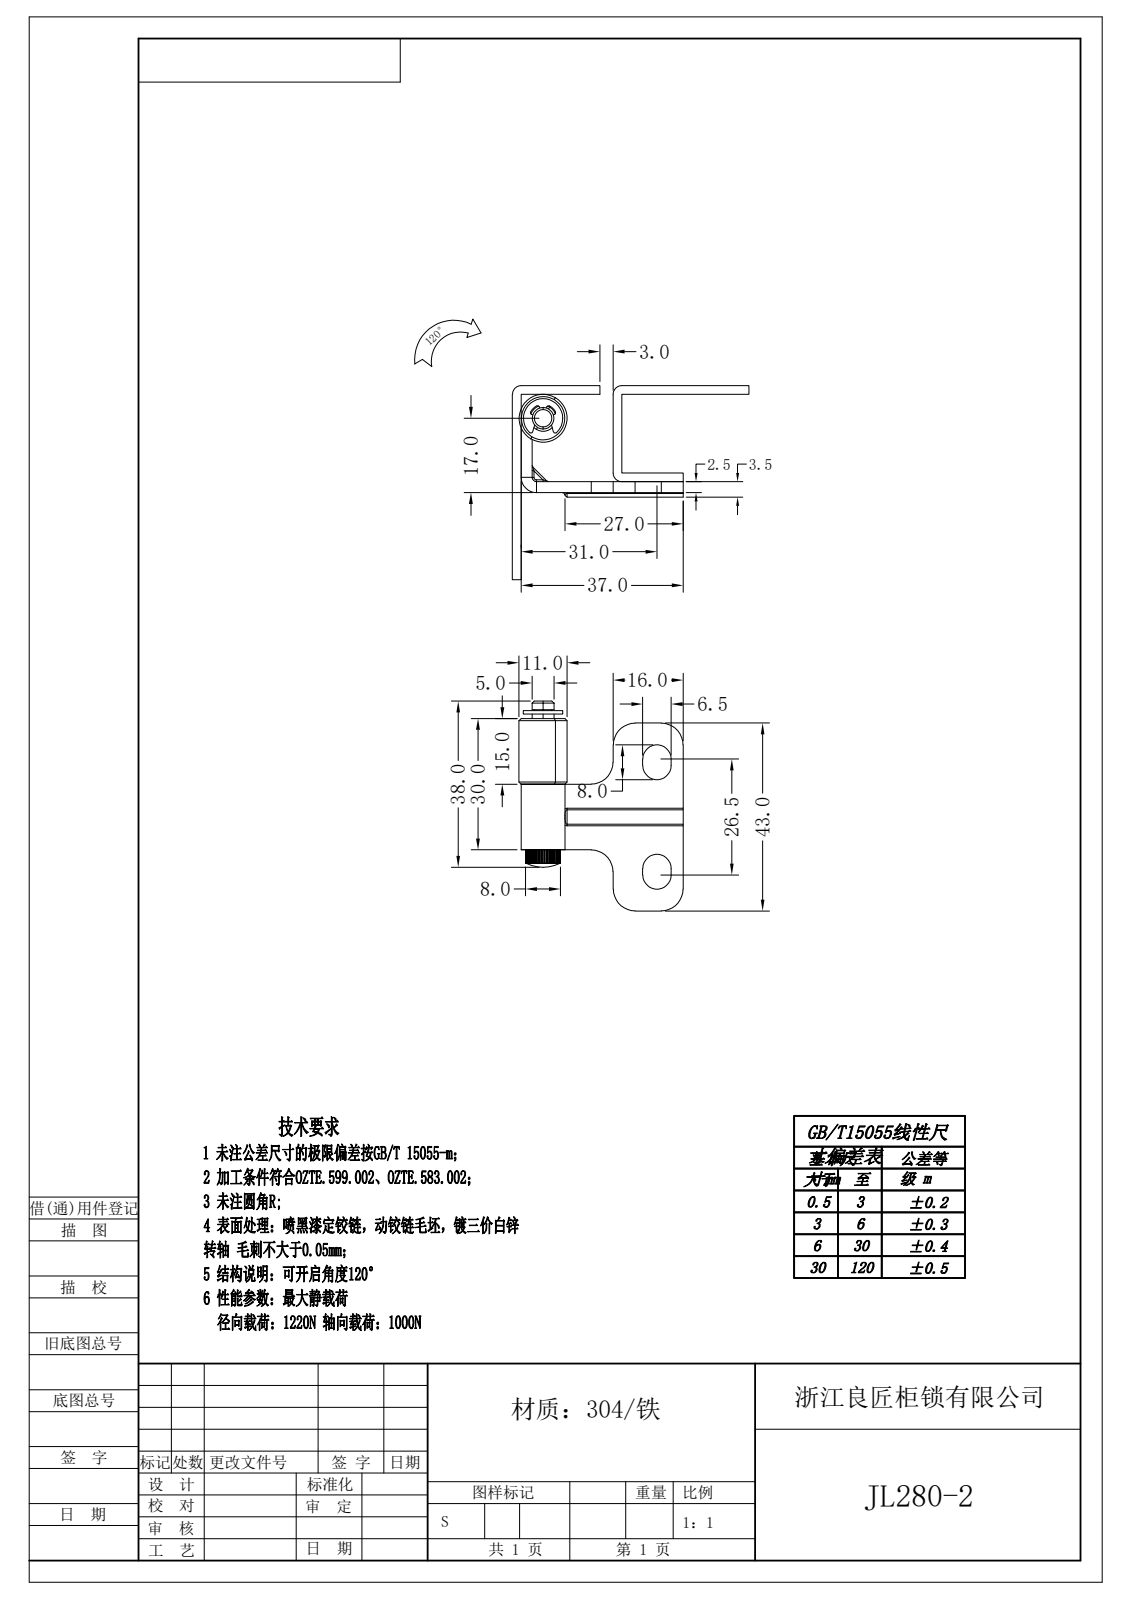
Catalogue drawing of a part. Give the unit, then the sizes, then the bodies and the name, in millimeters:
Units: millimetres
Overall size (bounding box): 48 × 37.5 × 24.12
Round holes (diameter × count): ⌀4 ×1
Round bosses / shafts (diameter × count): ⌀11 ×1, ⌀10 ×1, ⌀9 ×1, ⌀5 ×1
Partial cylindrical surfaces — rounded edges, fillets, slot ends (radius × count): R0.1 ×100, R0.5 ×14, R0.25 ×8, R5 ×6, R3.25 ×4, R1.62 ×2, R1 ×1, R2.5 ×1
Main face-to-face distances: 2.5, 15, 14.61, 37, 34.5, 16, 0.39, 29.61, 1.39, 16.39
Volume: 1 985 mm³ · Surface area: 5 294 mm²
Bodies: 3 solids, 314 faces (36 planar, 257 cylindrical, 21 other)
STEP written by: Rhino 8.5 (CONFIG_CONTROL_DESIGN)
